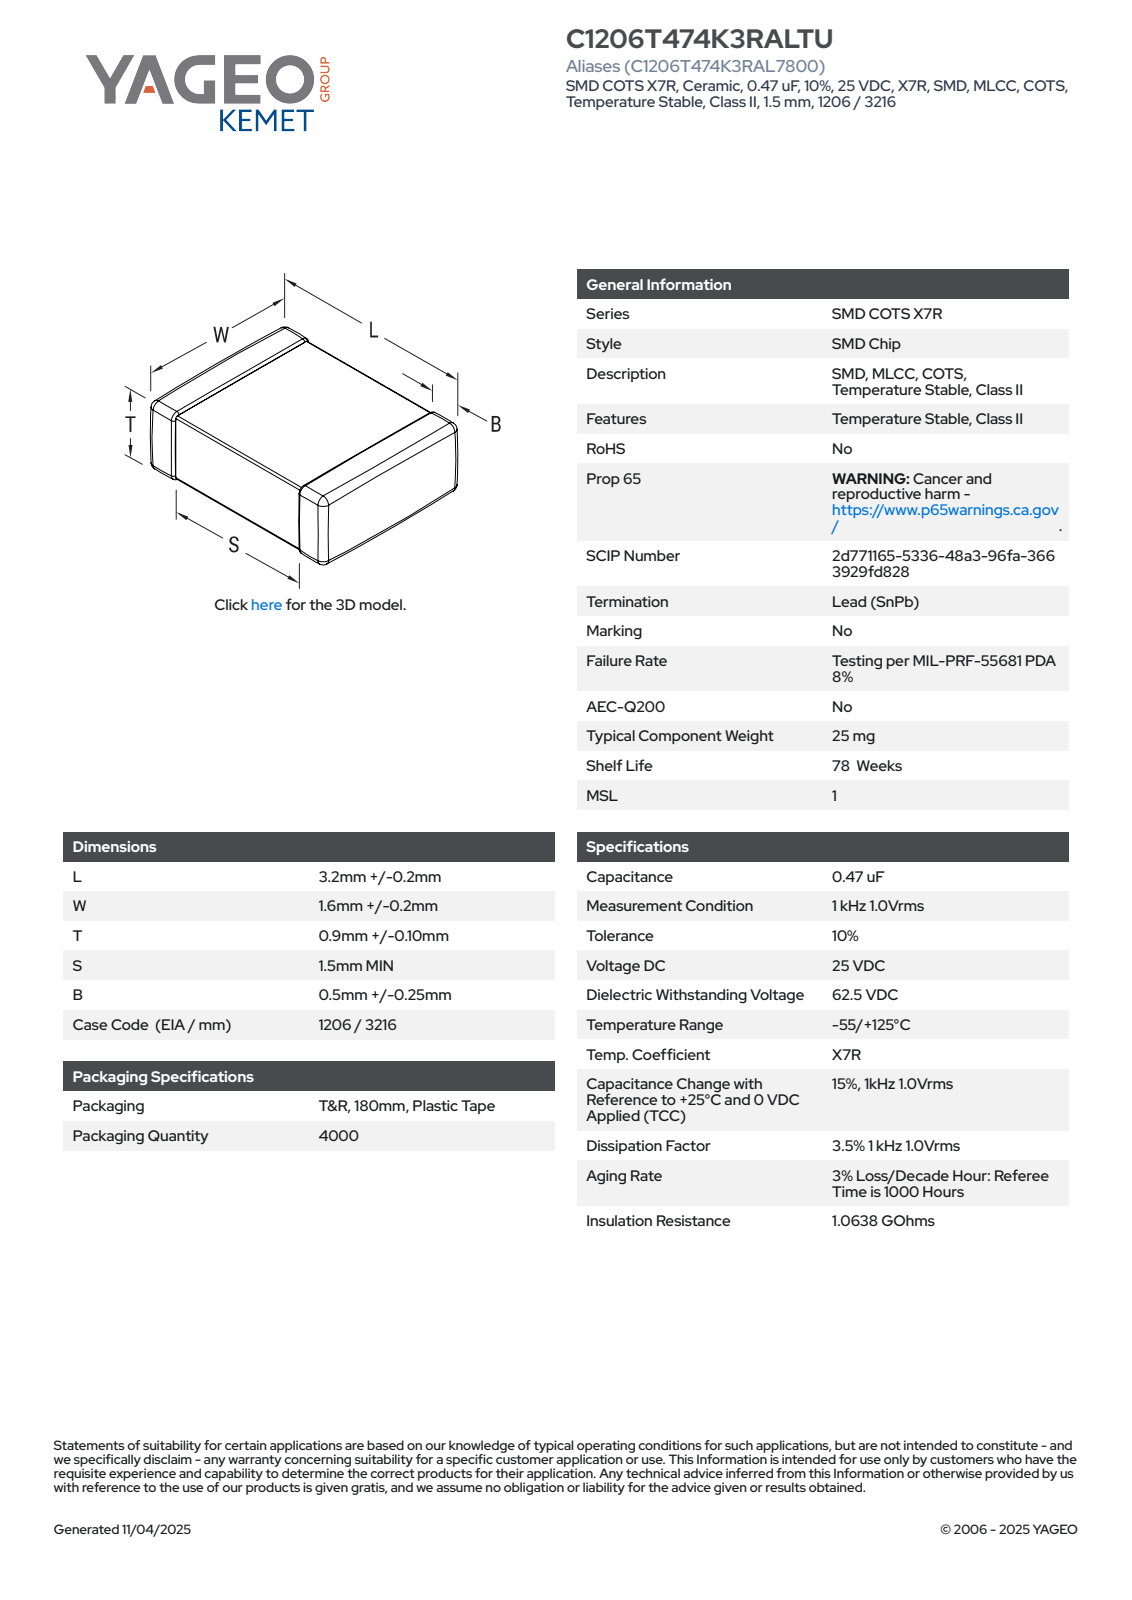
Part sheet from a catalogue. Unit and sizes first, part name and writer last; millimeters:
Units: millimetres
Overall size (bounding box): 3.4 × 1.8 × 1
Main face-to-face distances: 0.96, 0.92, 1.76, 1, 1.72, 3.4, 1.8, 0.97, 0.93, 1.57
Volume: 6 mm³ · Surface area: 22 mm²
Bodies: 4 solids, 125 faces (71 planar, 38 cylindrical, 16 other)
Part name (STEP PRODUCT): CCSM_STD_1206_L3.4W1.8T1S0.9B0.75
STEP written by: SolidWorks 2021 (AUTOMOTIVE_DESIGN)
